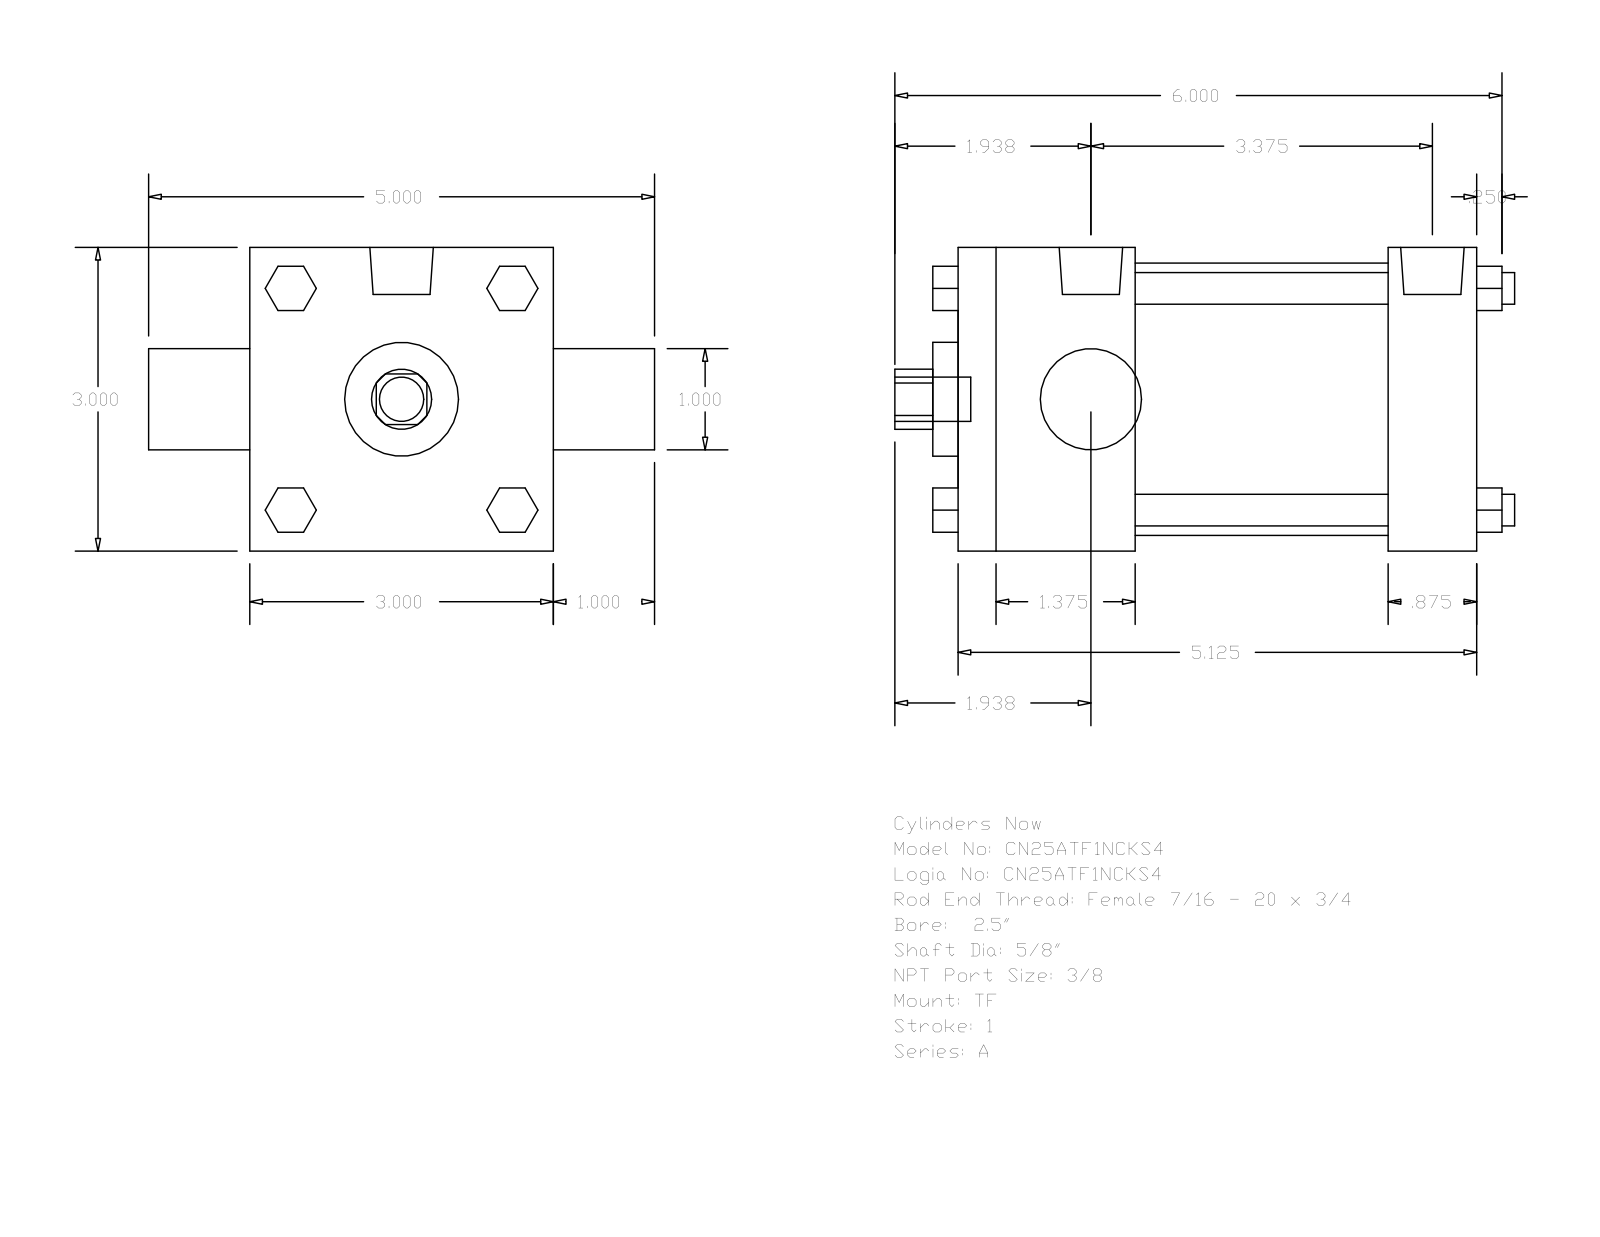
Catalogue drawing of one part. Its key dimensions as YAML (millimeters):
part_name: "A_TF__0250_0.625"
step_written_by: "GSSL Pune (CONFIG_CONTROL_DESIGN)"
units: millimeters
bodies: {solids: 0, faces: 120, planar: 92, cylindrical: 28, other: 0}
overall_size: [155.57, 127, 76.2]
round_holes:
  - {diameter: 15.88, count: 1}
  - {diameter: 25.4, count: 1}
  - {diameter: 28.57, count: 1}
  - {diameter: 68.33, count: 1}
round_bosses_or_shafts:
  - {diameter: 7.94, count: 4}
  - {diameter: 5.56, count: 3}
  - {diameter: 15.93, count: 2}
  - {diameter: 11.11, count: 1}
partial_cylinders:
  - {radius: 7.54, count: 1}
face_to_face_distances: [76.2, 130.17, 44.45, 107.95, 63.5, 85.72, 22.22, 25.4, 101.6, 136.52]
